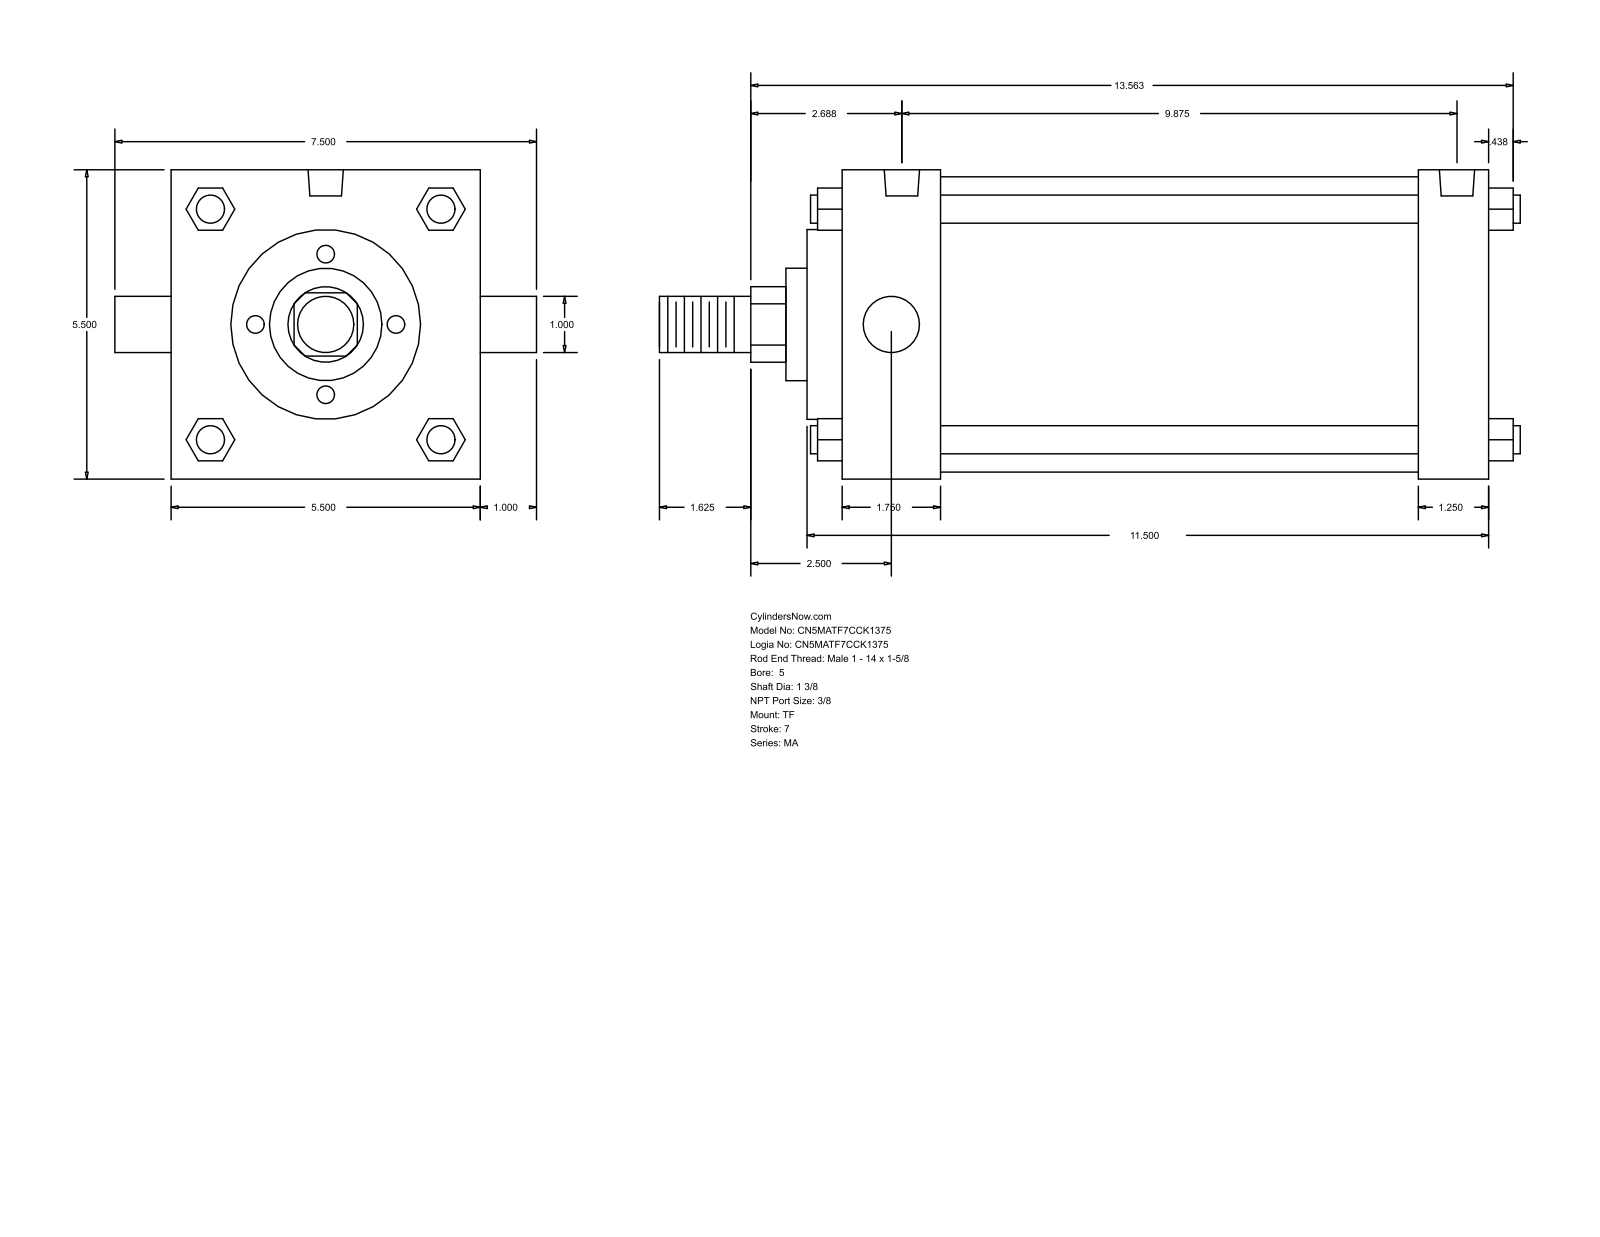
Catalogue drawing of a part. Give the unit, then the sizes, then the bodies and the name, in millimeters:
Units: millimetres
Overall size (bounding box): 388.94 × 190.5 × 139.7
Round holes (diameter × count): ⌀11.11 ×3, ⌀15.93 ×2
Round bosses / shafts (diameter × count): ⌀12.7 ×4, ⌀25.4 ×2, ⌀133.35 ×1, ⌀85.72 ×1, ⌀50.8 ×1, ⌀34.92 ×1
Partial cylindrical surfaces — rounded edges, fillets, slot ends (radius × count): R17.06 ×1
Main face-to-face distances: 139.7, 292.11, 260.35, 31.76, 44.45, 215.9, 247.66, 15.87, 60.32, 276.22
Hole centre spacings: 4.77, 246.06, 241.29, 250.83
Bodies: 0 solids, 122 faces (93 planar, 29 cylindrical, 0 other)
Part name (STEP PRODUCT): MA_TF__0500_1.375
STEP written by: GSSL Pune (CONFIG_CONTROL_DESIGN)
